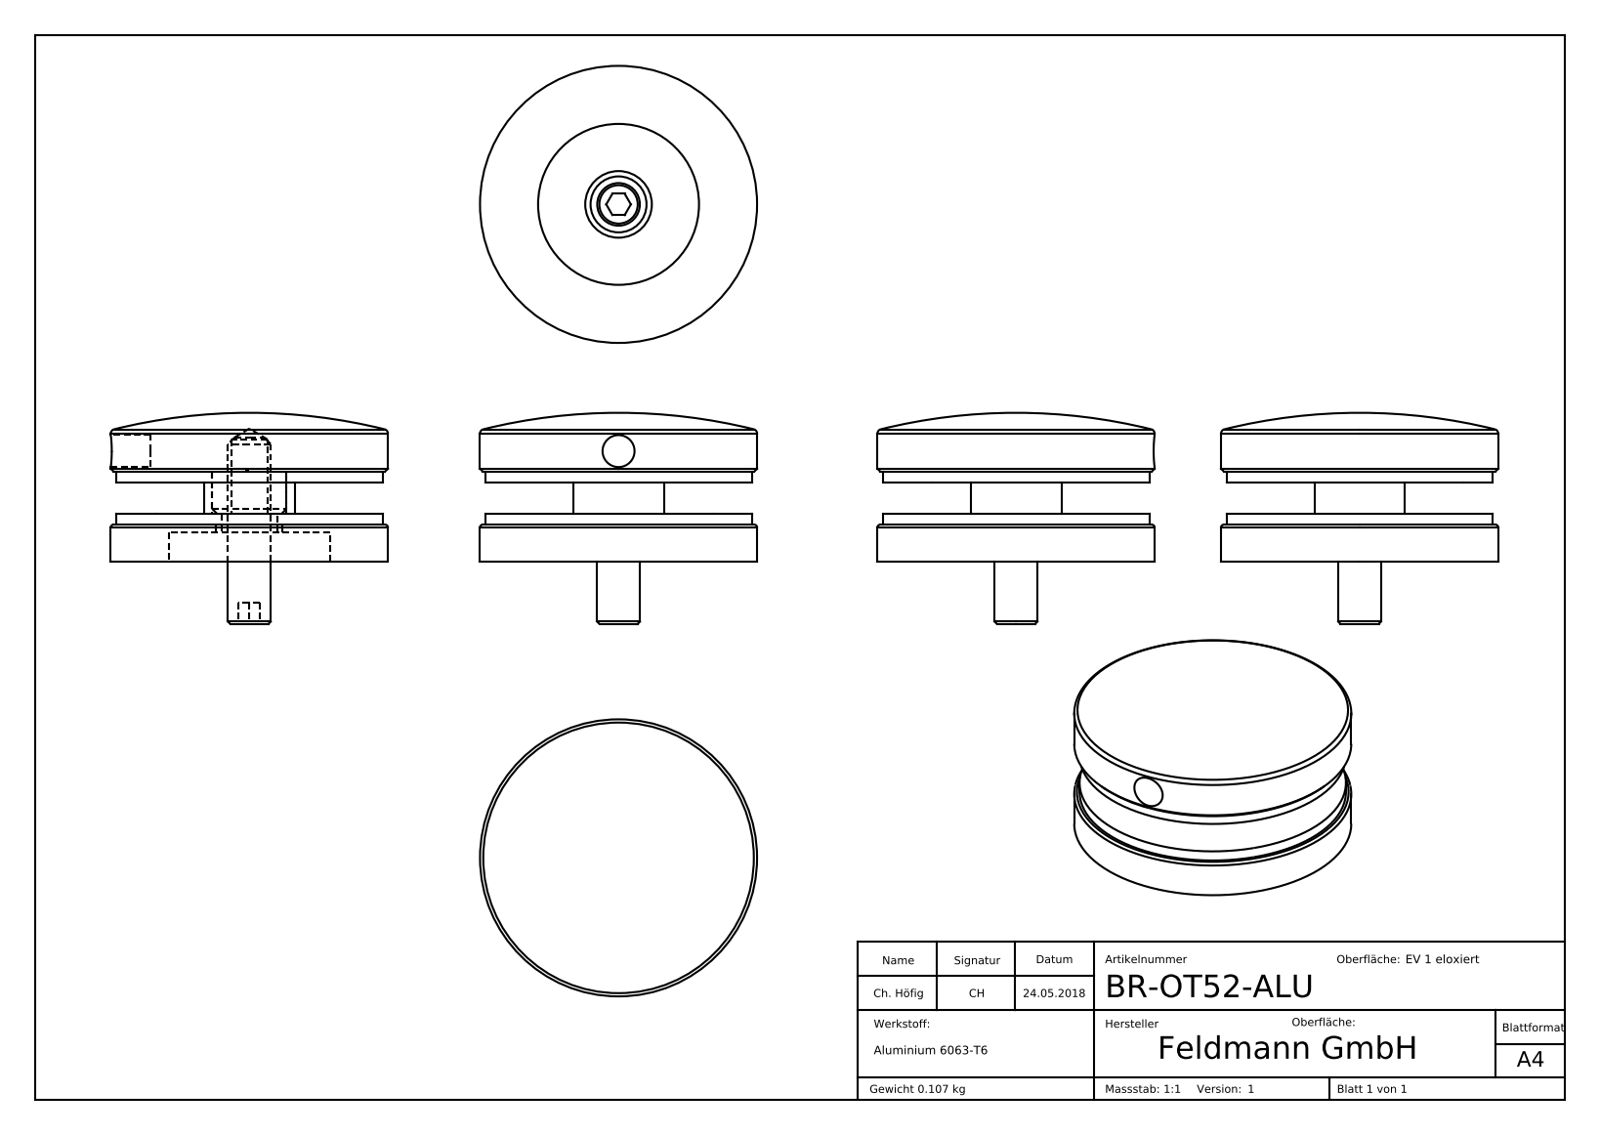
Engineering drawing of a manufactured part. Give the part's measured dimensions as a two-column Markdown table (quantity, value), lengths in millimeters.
| quantity | value |
| --- | --- |
| part name | BR-OT52-ALU; BR-OT52-XXX Teil2_BR-OT52-XXX Teil2; BR-OT52-XXX Teil1_BR-OT52-ALU Teil1; BR-OT52-XXX Teil4_BR-OT52-ALU Teil4 (+2 more) |
| STEP written by | SolidWorks 2015 (CONFIG_CONTROL_DESIGN) |
| units | millimeters |
| bodies | 5 solids, 308 faces (173 planar, 28 cylindrical, 107 other) |
| overall size | 52 × 52 × 39.61 |
| volume | 40 646 mm³ |
| surface area | 21 792 mm² |
| round holes (diameter × count) | 6 × 1, 6.8 × 1, 10.5 × 1, 12.5 × 1, 14 × 1, 30.2 × 1 |
| round bosses / shafts (diameter × count) | 52 × 1, 50 × 1, 17 × 1, 8 × 1 |
| main face-to-face distances | 2, 8, 10, 6, 7, 9, 15, 17, 5.5, 1.5 |
